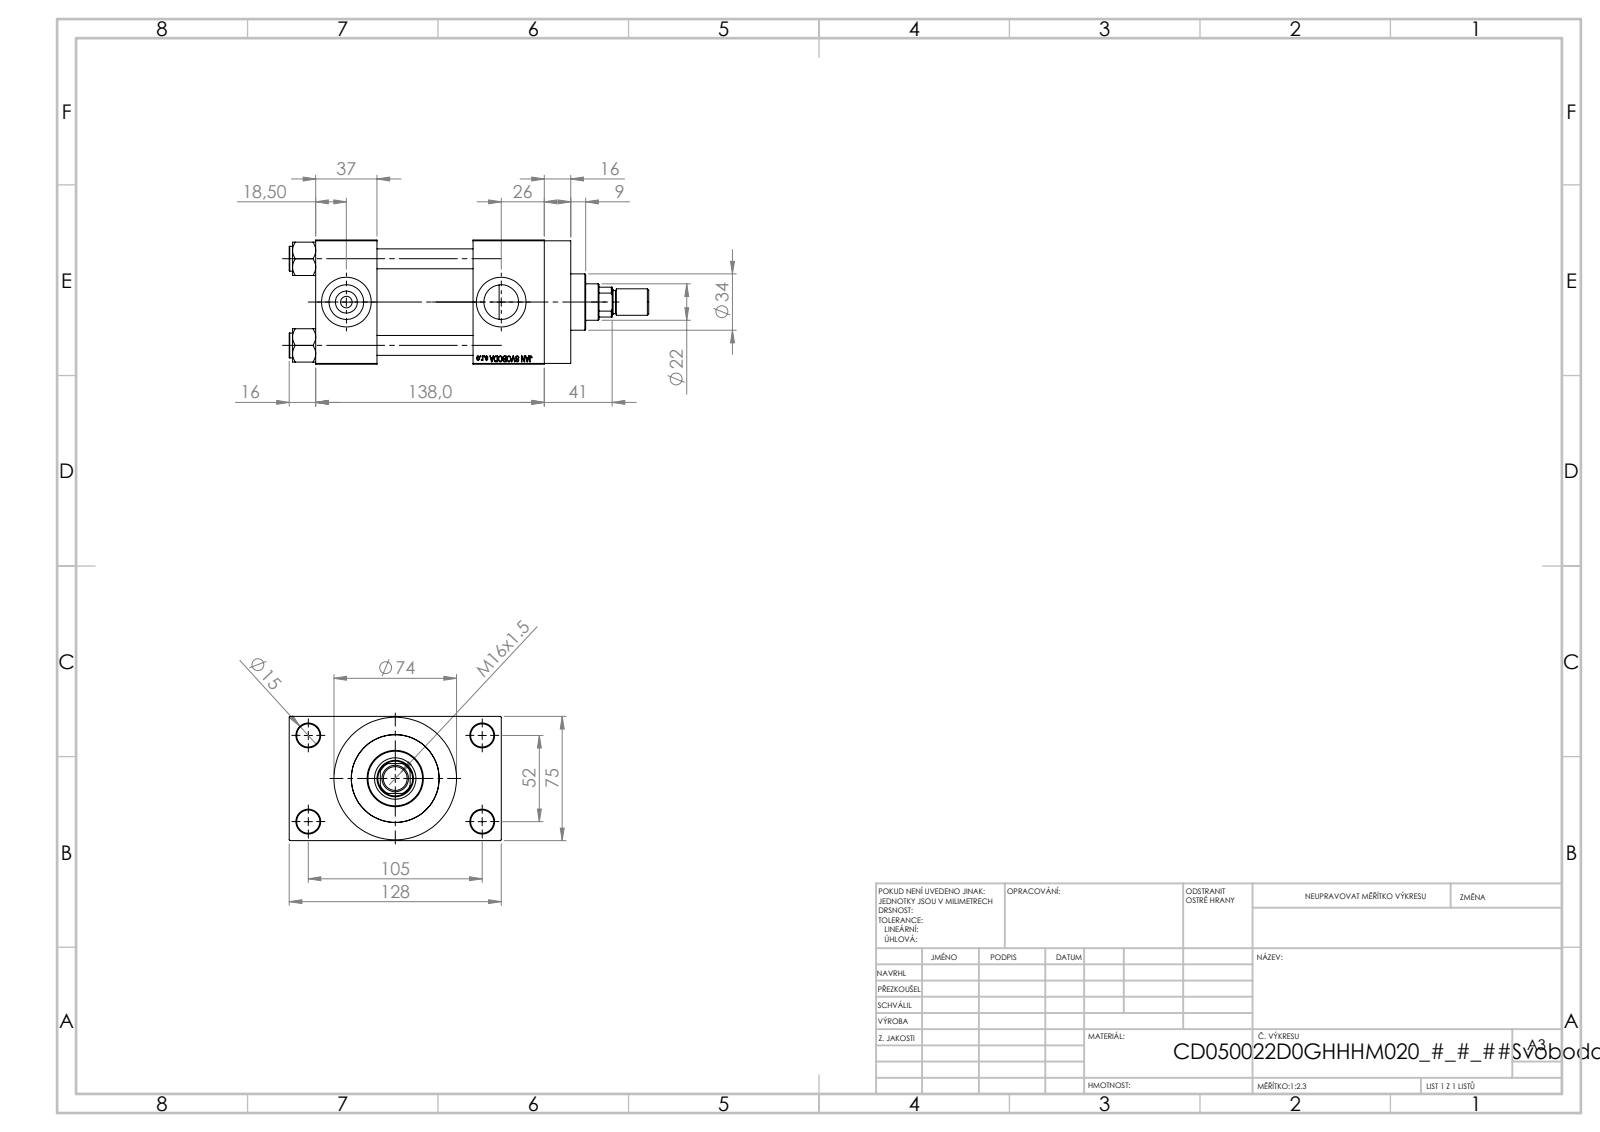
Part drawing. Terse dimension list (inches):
name: V215CD_D_Body; V215CD_VC_A; ROD_END_AH; V215CD_VCP_D (+2 more)
written by: SolidWorks 2019 (CONFIG_CONTROL_DESIGN)
unit: in
bodies: 12 solids, 1117 faces (501 planar, 92 cylindrical, 524 other)
size: 8.543 × 5.039 × 2.953
volume: 48.93 in³; area: 260.8 in²
holes: 4× ⌀0.472, 4× ⌀0.551, 2× ⌀0.276, 2× ⌀0.825, 2× ⌀1.181, 1× ⌀0.413, 1× ⌀0.866, 1× ⌀0.984, 1× ⌀1.614, 1× ⌀1.969, 1× ⌀2.087
bosses: 4× ⌀0.591, 1× ⌀2.913, 1× ⌀2.205, 1× ⌀1.339, 1× ⌀0.63, 1× ⌀0.551
rounds: 1× R0.413
face distances: 2.953, 2.283, 1.457, 3.74, 1.043, 5.433, 3.976, 1.693, 3.996, 0.63
hole spacings: 1.037, 1.456, 2.059, 2.3, 2.307, 3.096, 3.715, 2.047
